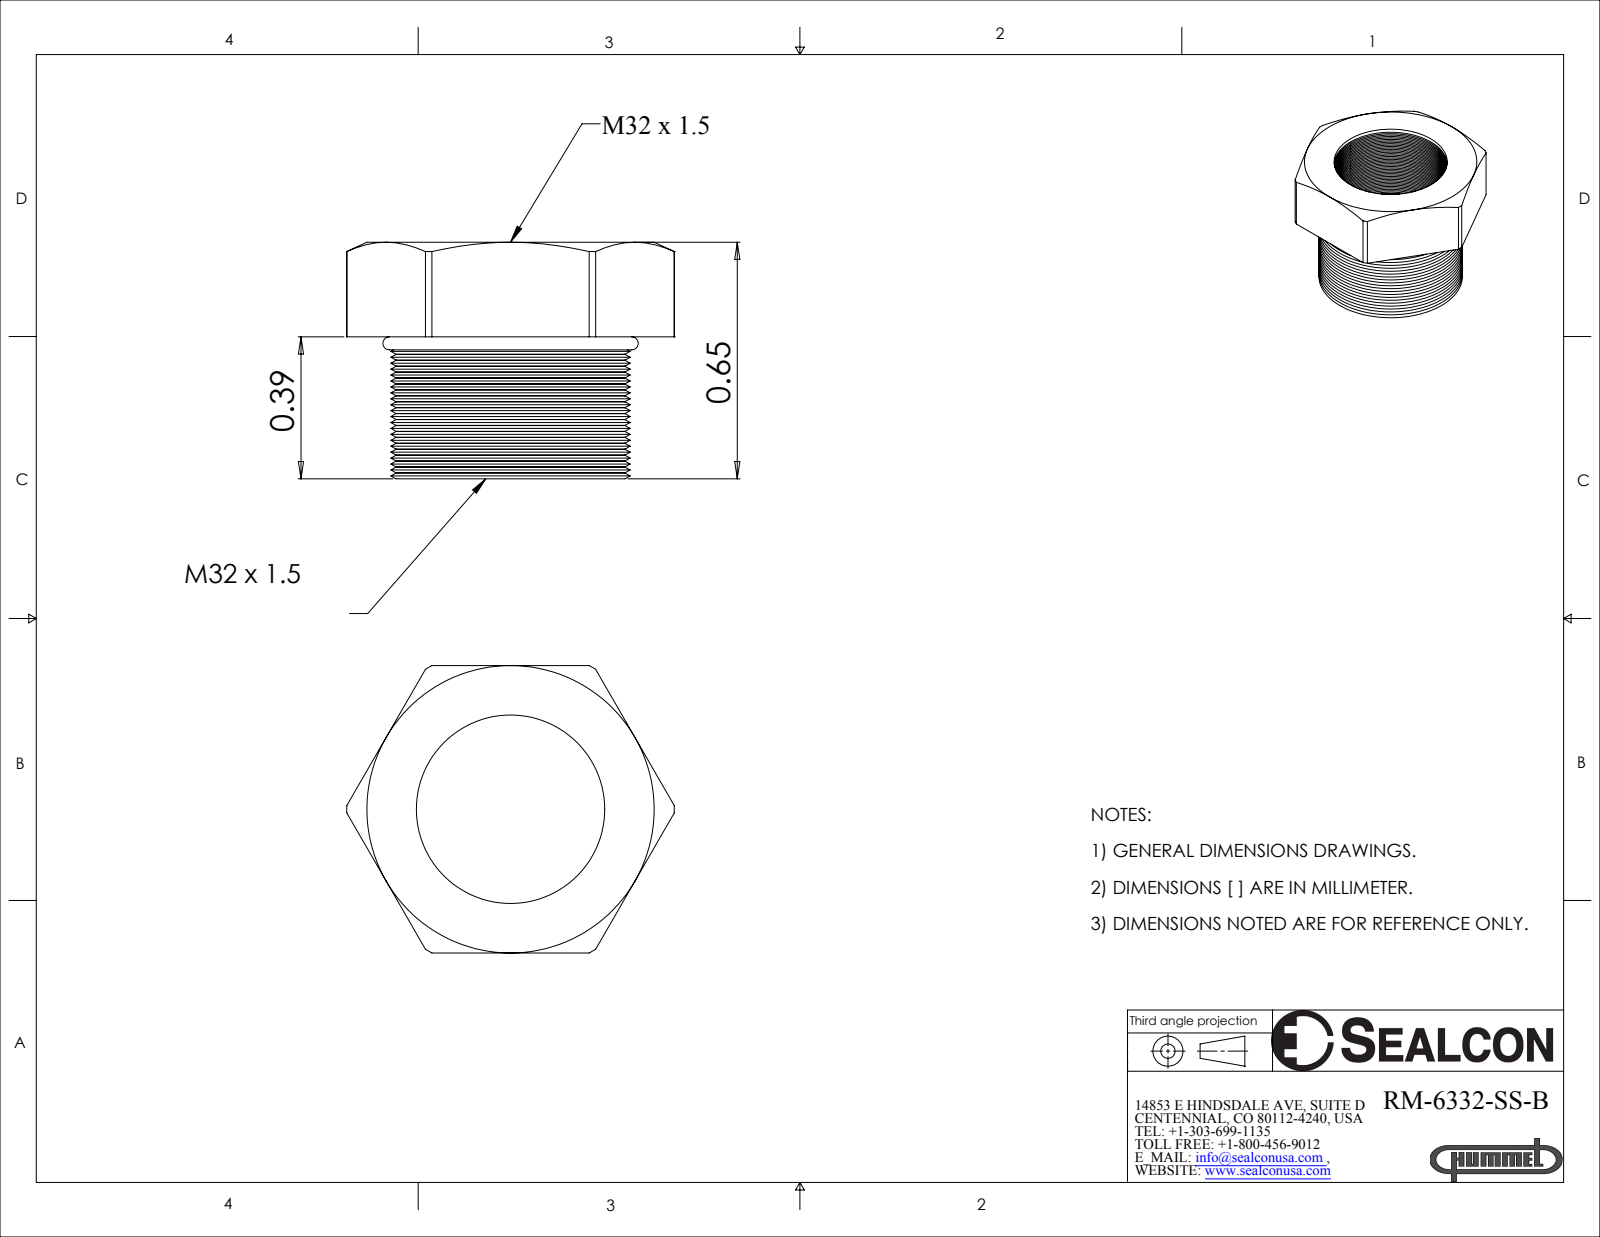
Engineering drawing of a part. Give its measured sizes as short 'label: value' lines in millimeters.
name: RM-6332-SS-B
written by: SolidWorks 2008 (CONFIG_CONTROL_DESIGN)
unit: mm
bodies: 2 solids, 403 faces (9 planar, 135 cylindrical, 259 other)
size: 22.9 × 20.1 × 16.5
volume: 2 110 mm³; area: 3 374 mm²
holes: 1× ⌀13.2
bosses: 1× ⌀16
rounds: 1× R11.4
face distances: 20.1, 6.6, 9.9, 16.5
